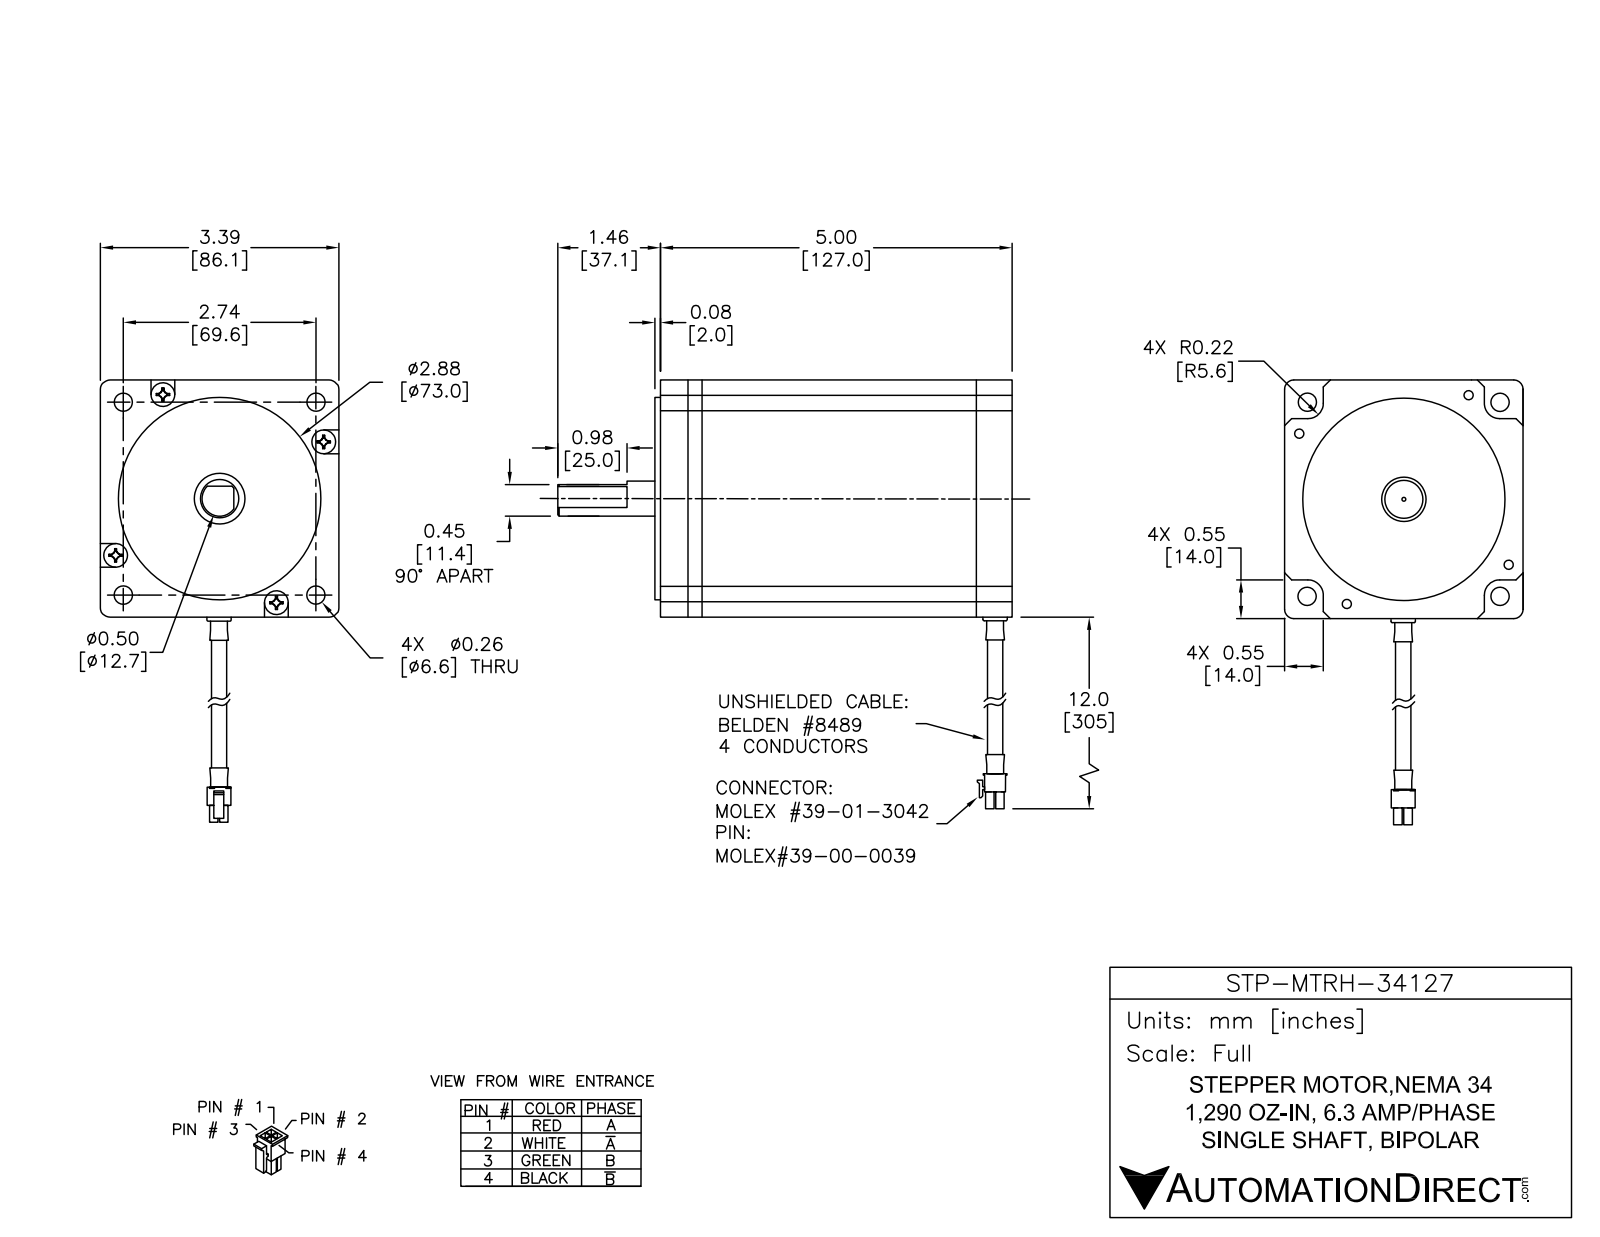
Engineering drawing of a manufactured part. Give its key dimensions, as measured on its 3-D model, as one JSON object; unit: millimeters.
{"part_name": "STP-MTRH-34127", "step_written_by": "SolidWorks 2014 (AUTOMOTIVE_DESIGN)", "units": "millimeters", "bodies": {"solids": 19, "faces": 3298, "planar": 1191, "cylindrical": 1970, "other": 137}, "overall_size": [389.3, 163.9, 85.8], "volume_mm3": 606600, "surface_area_mm2": 246100, "round_holes": [[2.8, 4], [4.2, 4], [4.5, 4], [6.6, 4], [1, 1], [8, 1], [15, 1], [16.1, 1], [17.2, 1], [17.4, 1], [18.3, 1], [25.9, 1]], "round_bosses_or_shafts": [[1.3, 6], [4.2, 4], [3.5, 4], [80.5, 1], [80.4, 1], [79.8, 1], [73, 1], [55.4, 1]], "partial_cylinders_radius": [[0.3, 312], [1.5, 48], [0.9, 32], [1.4, 32], [0.5, 16], [2.8, 4], [3, 4], [4.2, 4]], "face_to_face_distances": [85.8, 71.2, 14.6, 38.3, 47.5, 23.7, 32.9, 9.2, 1.5, 2], "hole_center_spacings": [11.5, 45, 49.2, 58.8, 63.7, 69.6, 73.8, 93.6]}
